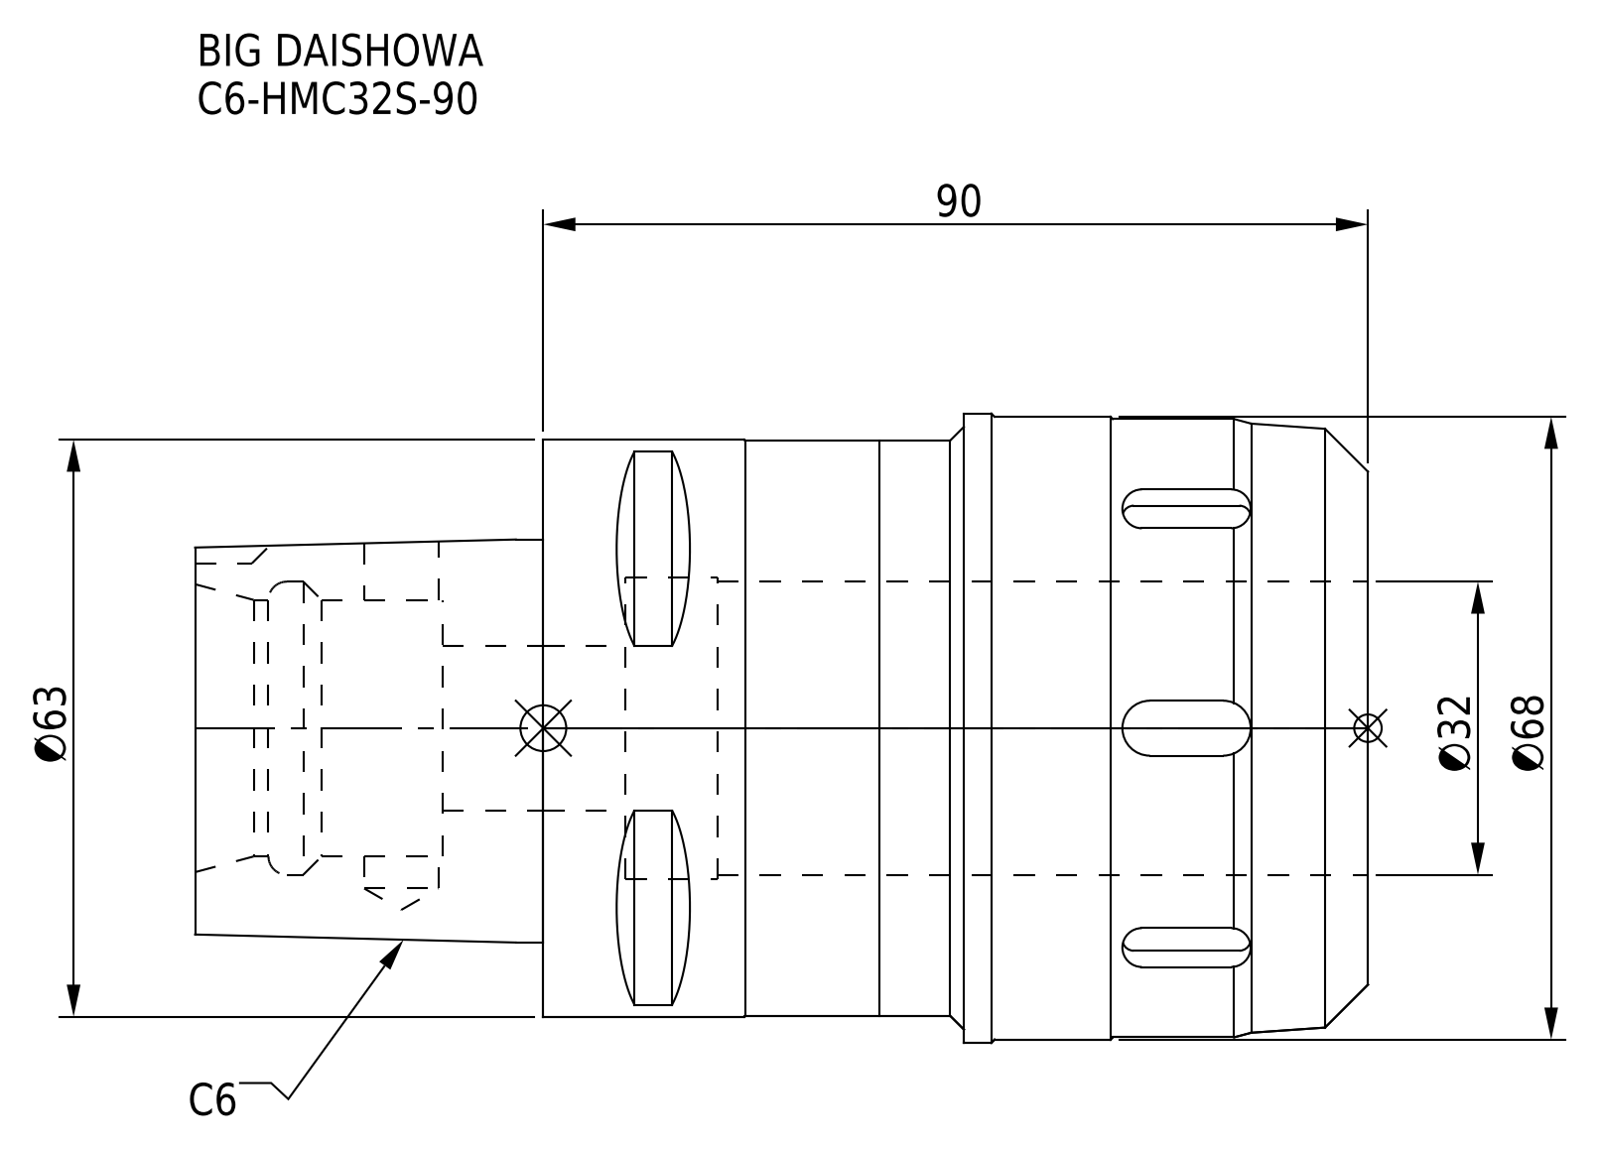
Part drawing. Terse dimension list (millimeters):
name: C6-HMC32S-90
written by: CREO PARAMETRIC BY PTC INC, 2016380 (AUTOMOTIVE_DESIGN)
unit: mm
bodies: 1 solid, 120 faces (53 planar, 43 cylindrical, 24 other)
size: 128 × 68.7 × 68.7
volume: 259 932 mm³; area: 42 292 mm²
holes: 1× ⌀8.1, 1× ⌀18, 1× ⌀28, 1× ⌀32, 1× ⌀33
bosses: 1× ⌀68.7, 1× ⌀68, 1× ⌀67.5, 1× ⌀63, 1× ⌀62.8
rounds: 12× R3, 1× R5
face distances: 90, 81, 9, 128, 47, 38, 101, 20, 11, 27
